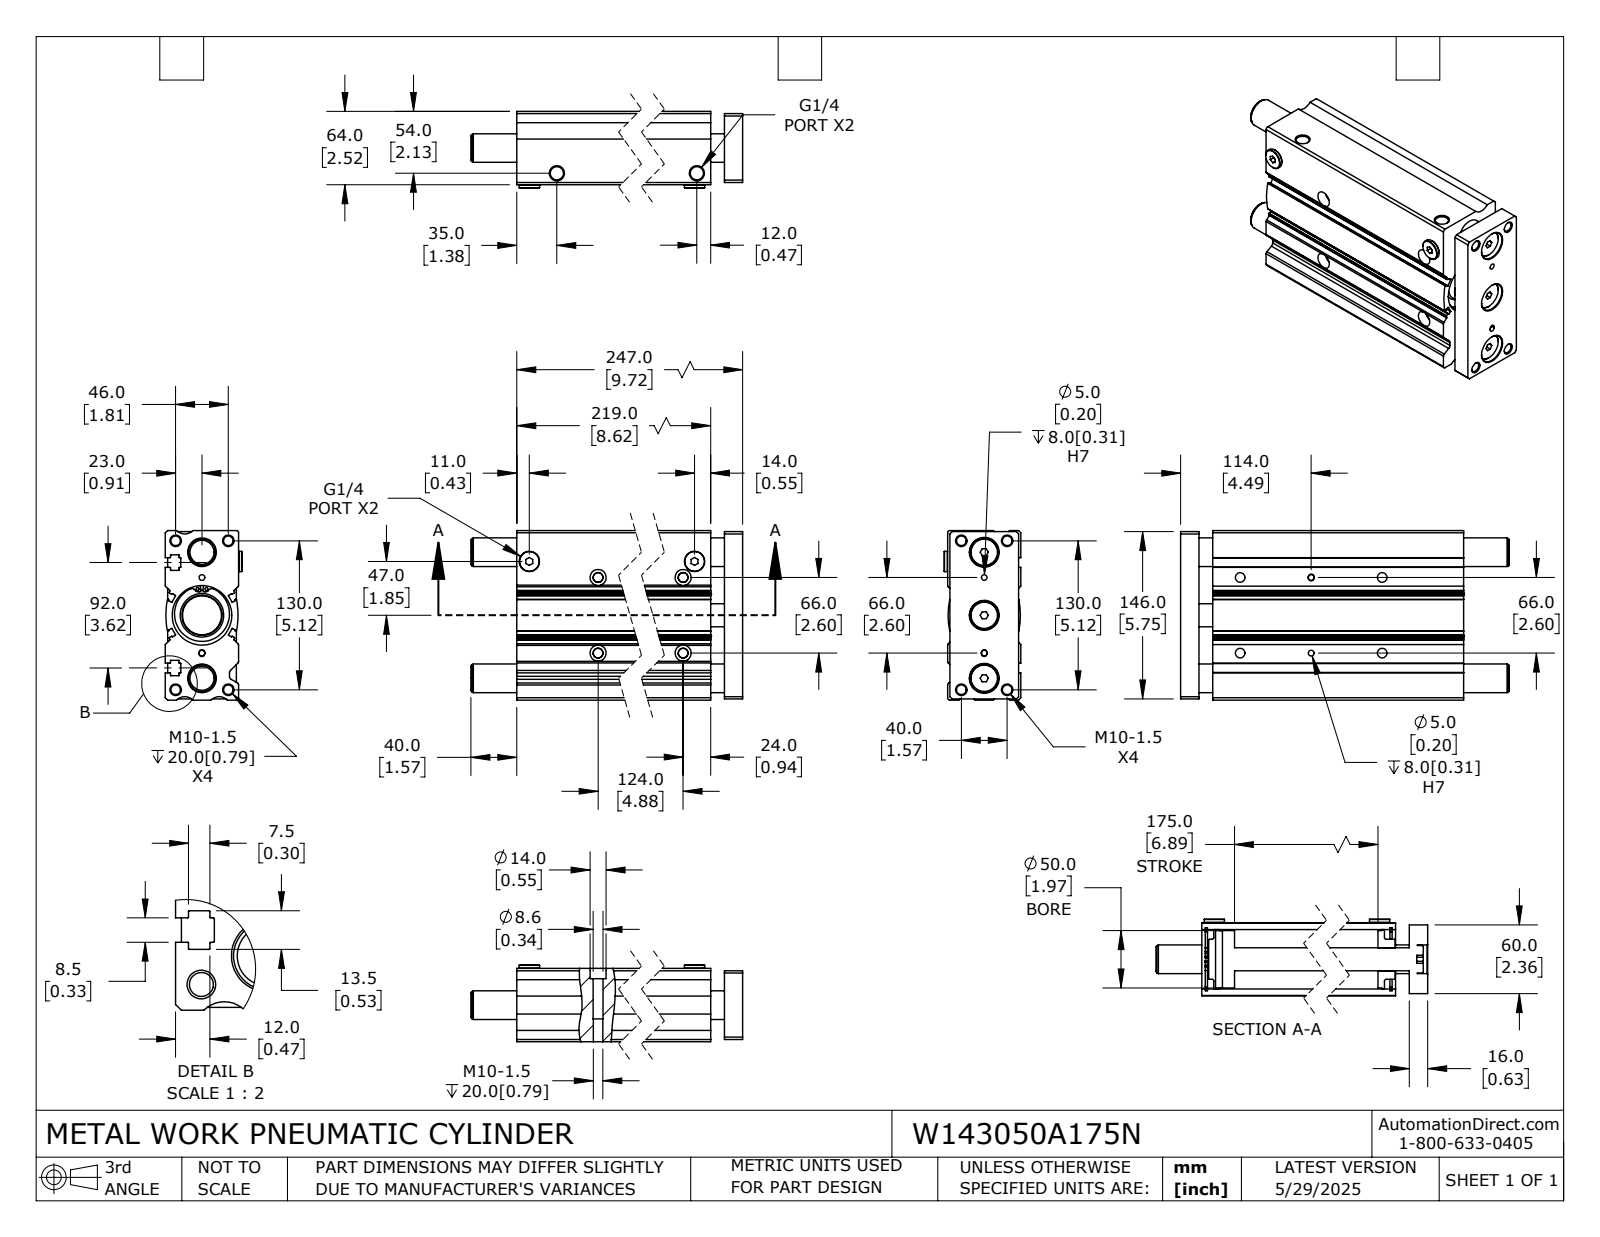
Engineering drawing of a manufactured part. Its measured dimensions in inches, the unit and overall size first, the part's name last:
Units: inches
Overall size (bounding box): 11.299 × 5.827 × 2.638
Round holes (diameter × count): ⌀0.33 ×12, ⌀0.098 ×4, ⌀0.197 ×4, ⌀0.339 ×4, ⌀0.551 ×4, ⌀0.984 ×3, ⌀0.451 ×2, ⌀1.89 ×2, ⌀0.787 ×1
Round bosses / shafts (diameter × count): ⌀0.945 ×3, ⌀0.697 ×2, ⌀2.165 ×1, ⌀2.047 ×1, ⌀1.969 ×1, ⌀1.378 ×1
Partial cylindrical surfaces — rounded edges, fillets, slot ends (radius × count): R0.012 ×44, R0.02 ×12, R0.118 ×10, R0.079 ×6, R2.677 ×6, R0.039 ×4, R0.098 ×4, R0.394 ×3
Main face-to-face distances: 2.52, 0.472, 8.622, 0.63, 5.827, 0.098, 0.531, 9.094, 0.079, 1.102
Hole centre spacings: 0.118, 0.424, 0.869, 0.88, 0.916, 0.963, 0.987, 1.271
Volume: 105.1 in³ · Surface area: 497.4 in²
Bodies: 6 solids, 466 faces (186 planar, 224 cylindrical, 56 other)
Part name (STEP PRODUCT): W143050A175N_ROD; W143050A175N; W143050A175N_BODY
STEP written by: SolidWorks 2024 (CONFIG_CONTROL_DESIGN)
